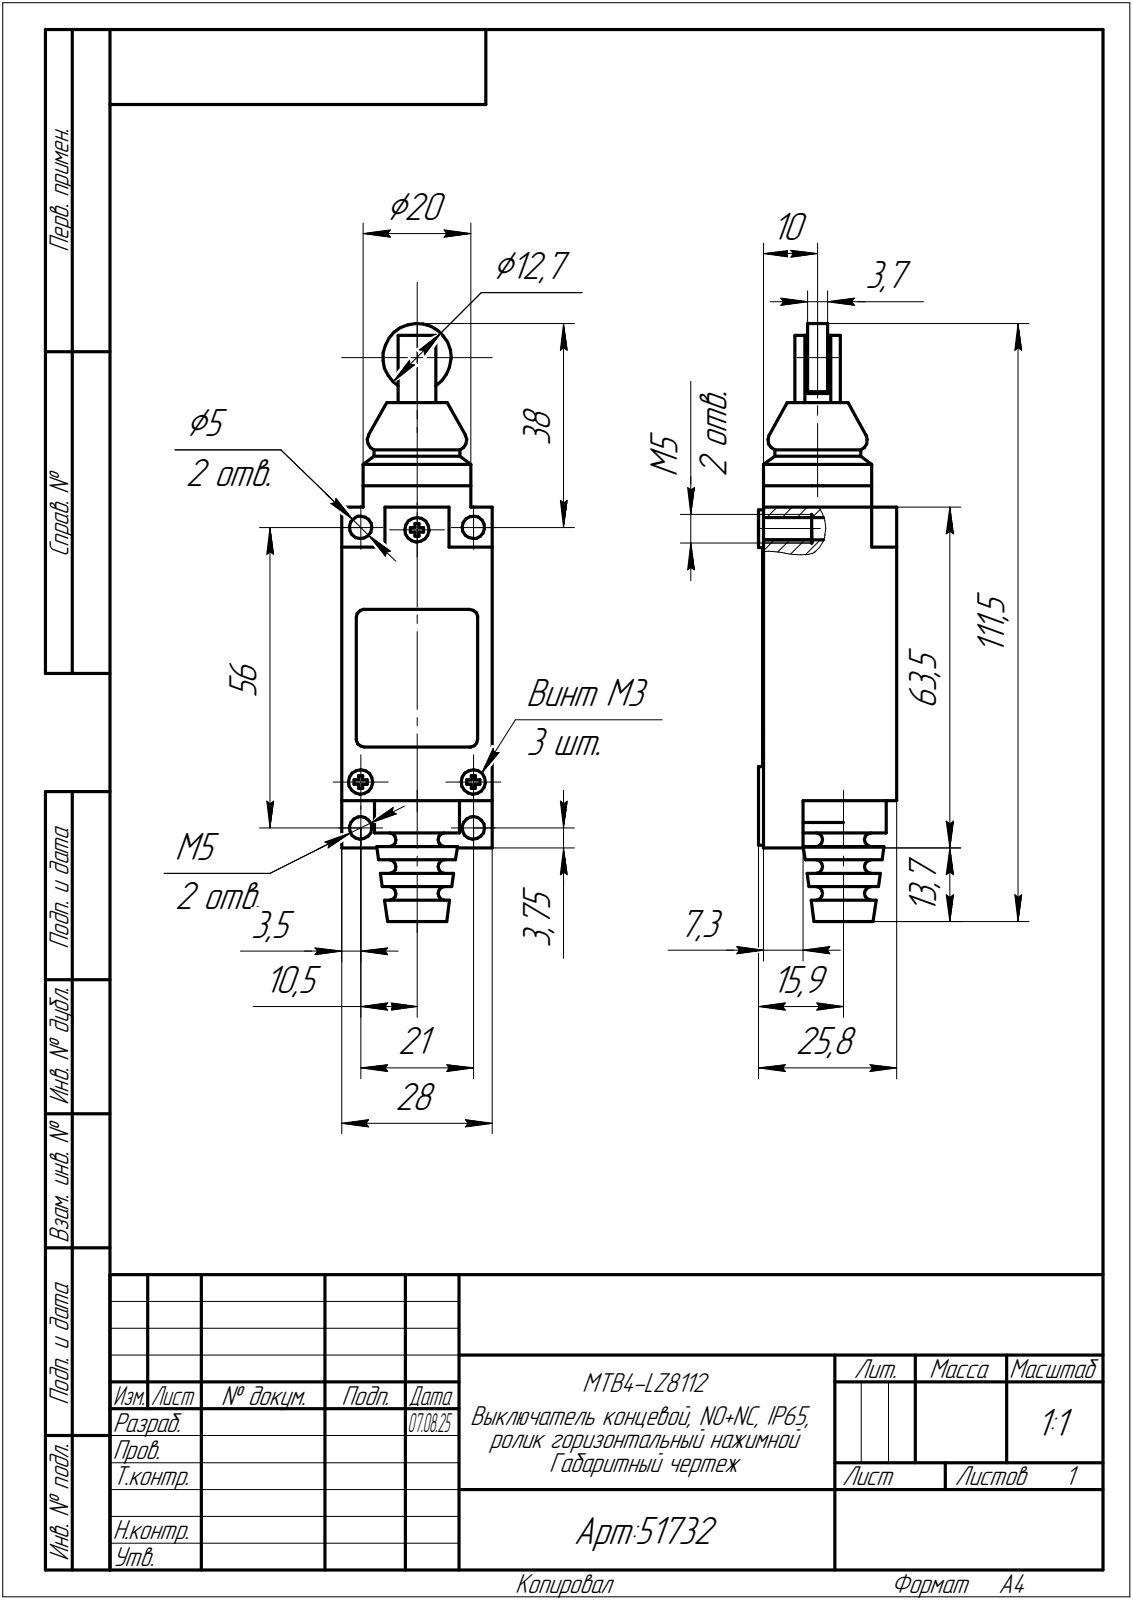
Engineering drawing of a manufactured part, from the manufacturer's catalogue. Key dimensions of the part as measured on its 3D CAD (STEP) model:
Part name (STEP PRODUCT): MTB4-LZ8112
STEP written by: C3D Toolkit (CONFIG_CONTROL_DESIGN)
Units: millimetres
Bodies: 2 solids, 441 faces (405 planar, 21 cylindrical, 15 other)
Overall size (bounding box): 111.45 × 28 × 25.8
Volume: 46 740 mm³ · Surface area: 12 242 mm²
Round holes (diameter × count): ⌀4.2 ×4, ⌀6.2 ×3, ⌀6 ×1
Round bosses / shafts (diameter × count): ⌀5 ×3, ⌀20.1 ×1, ⌀16 ×1, ⌀15.8 ×1, ⌀12.7 ×1
Partial cylindrical surfaces — rounded edges, fillets, slot ends (radius × count): R1.5 ×4, R4.25 ×1
Main face-to-face distances: 28, 24.8, 24.6, 4, 7.5, 2.5, 11.9, 12.9, 8.2, 4.7
Hole centre spacings: 21, 8.55, 10.51, 22.67, 47.45, 48.16, 51.89, 56
